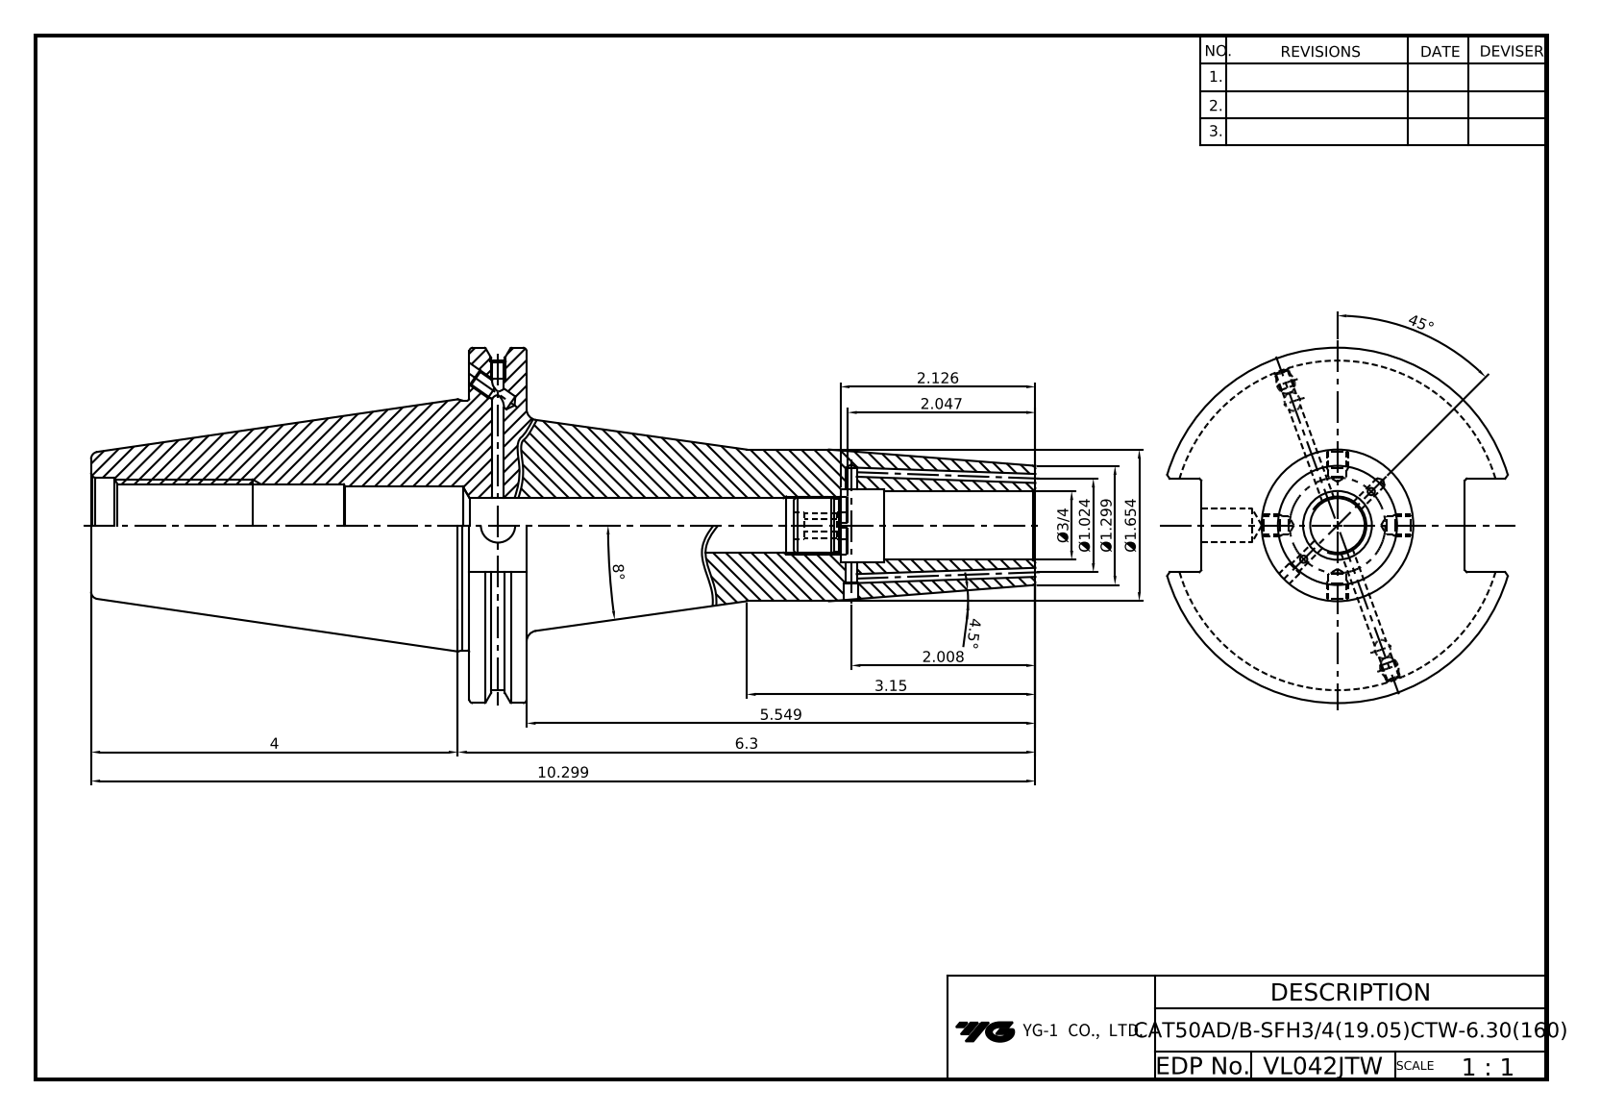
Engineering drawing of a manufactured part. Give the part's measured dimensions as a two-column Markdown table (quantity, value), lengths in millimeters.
| quantity | value |
| --- | --- |
| part name | CAT50_SHANK_20130708 |
| STEP written by | CREO PARAMETRIC BY PTC INC, 2018500 (CONFIG_CONTROL_DESIGN) |
| units | millimeters |
| bodies | 1 solid, 98 faces (30 planar, 28 cylindrical, 40 other) |
| overall size | 261.75 × 98.42 × 94.43 |
| volume | 510 164 mm³ |
| surface area | 71 657 mm² |
| round holes (diameter × count) | 9.53 × 1, 16 × 1, 19.05 × 1, 20.25 × 1, 20.5 × 1, 21 × 1, 24 × 1, 25 × 1, 25.6 × 1 |
| round bosses / shafts (diameter × count) | 98.42 × 1, 91.29 × 1, 69.25 × 1, 42 × 1 |
| main face-to-face distances | 15.9, 156.85, 140.95, 104.9, 120.8, 261.75, 73.03, 25.7, 110.99, 6.09 |
